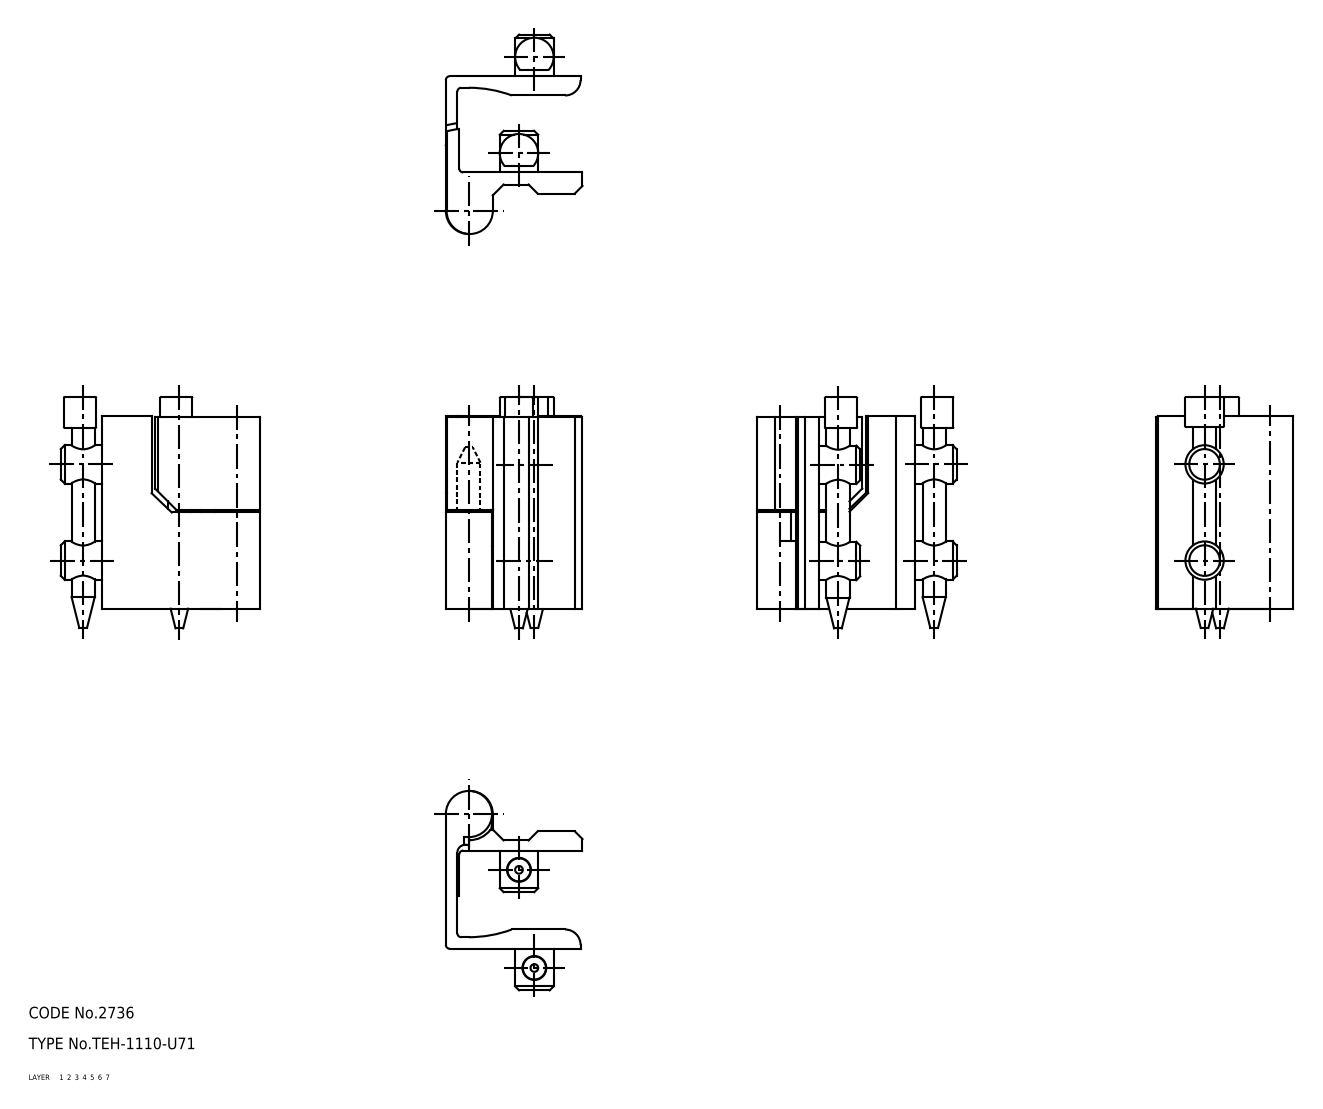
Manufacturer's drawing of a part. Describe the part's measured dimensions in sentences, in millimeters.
The part is named "pin_mr-1; washer_mr; shaft_mr; pin_mr (+3 more)". Its 3-D file was written by "CADfix (AUTOMOTIVE_DESIGN)". It is 6 solids with 126 faces: 0 planar, 0 cylindrical and 126 other. Overall it measures 60.1 by 51.8 by 35.5 millimeters. Its volume is 29 295 cubic millimeters and its surface area 18 382 square millimeters.
